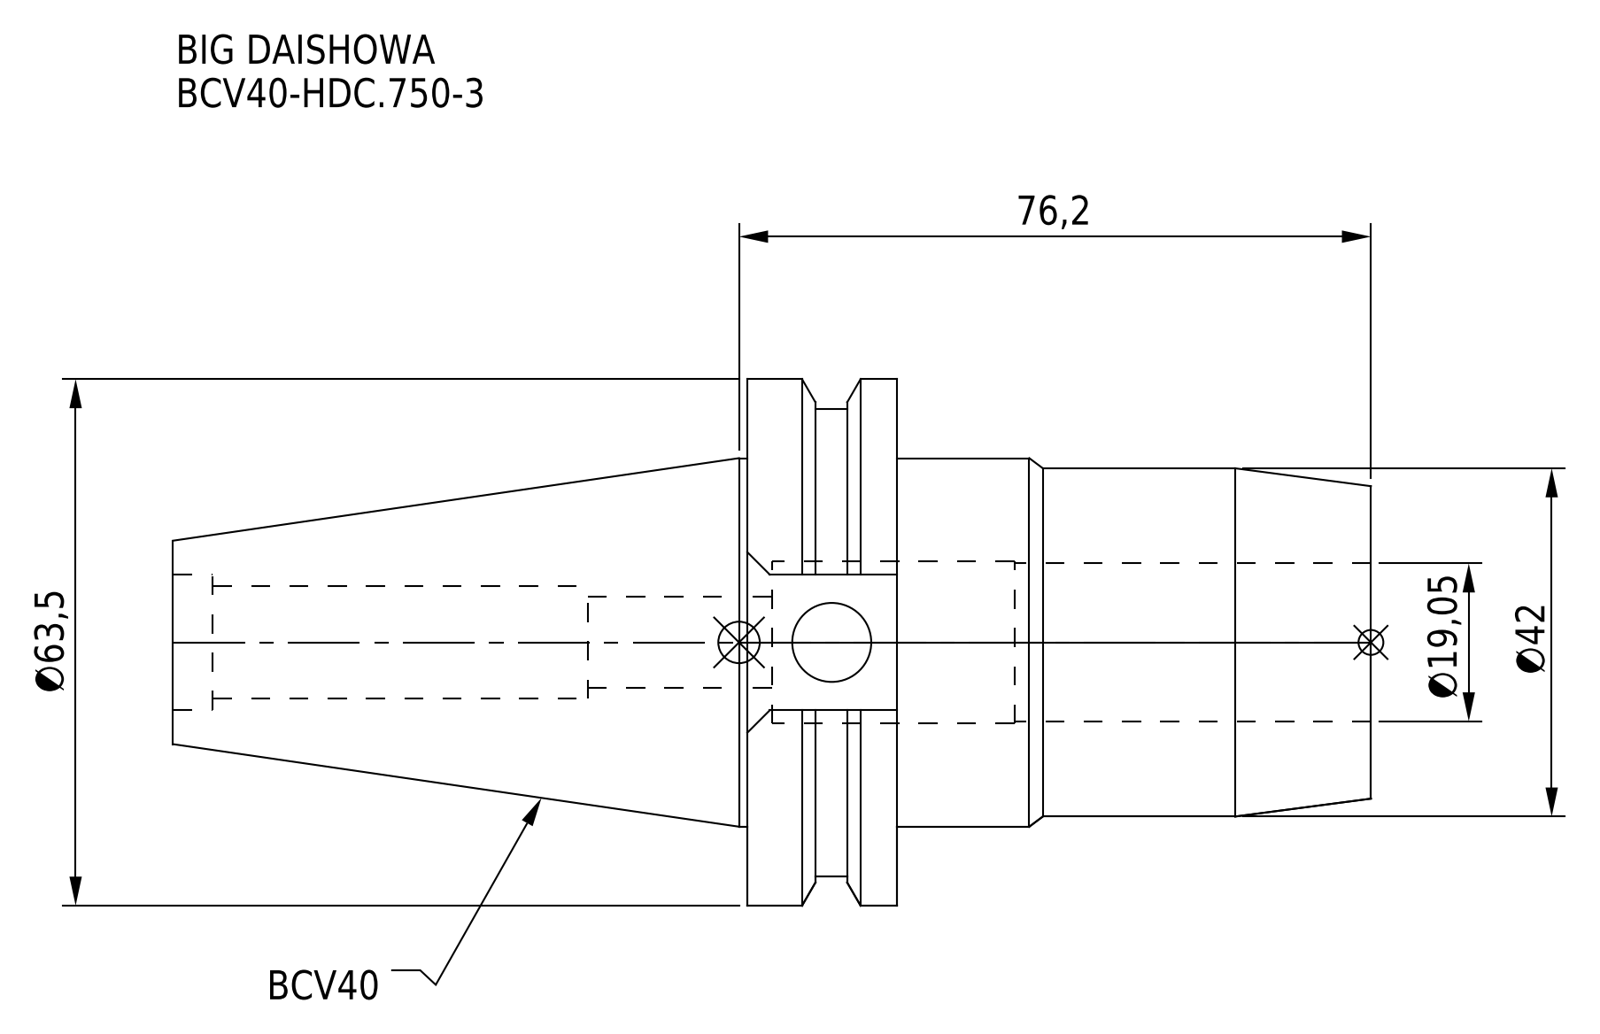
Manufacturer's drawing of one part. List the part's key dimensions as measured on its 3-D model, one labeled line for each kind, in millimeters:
Part name (STEP PRODUCT): BCV40-HDC_750-3
STEP written by: CREO PARAMETRIC BY PTC INC, 2016380 (AUTOMOTIVE_DESIGN)
Units: millimetres
Bodies: 1 solid, 59 faces (23 planar, 26 cylindrical, 10 other)
Overall size (bounding box): 144.45 × 63.5 × 61.35
Volume: 165 771 mm³ · Surface area: 31 331 mm²
Round holes (diameter × count): ⌀9.53 ×1, ⌀11 ×1, ⌀13.6 ×1, ⌀16.32 ×1, ⌀19.05 ×1, ⌀19.6 ×1
Round bosses / shafts (diameter × count): ⌀63.5 ×1, ⌀56.36 ×1, ⌀44.45 ×1, ⌀42 ×1
Main face-to-face distances: 18.05, 57.15, 75.2, 144.45, 87.3, 69.25, 47.55, 72.2, 15.05, 3
